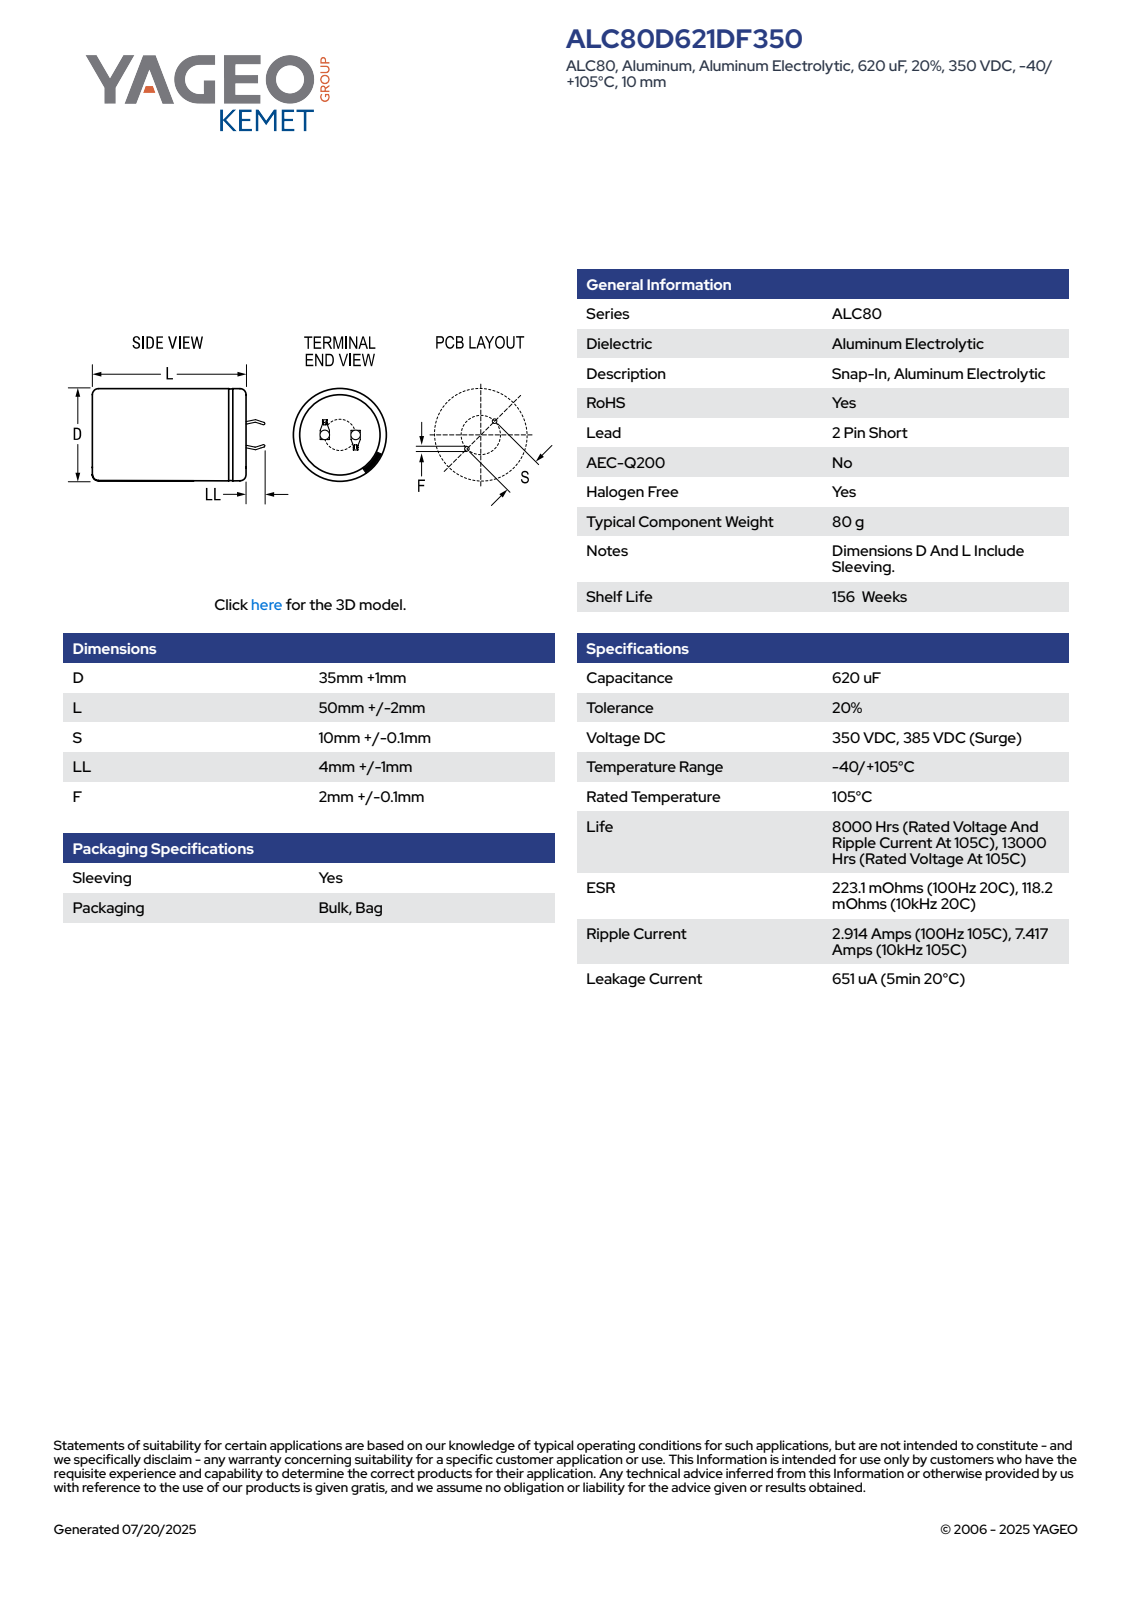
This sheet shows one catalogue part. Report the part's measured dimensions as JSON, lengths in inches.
{"part_name": "CARS_K2P_35X50_D36L52S10LL5F2.1", "step_written_by": "SolidWorks 2014 (AUTOMOTIVE_DESIGN)", "units": "inches", "bodies": {"solids": 1, "faces": 100, "planar": 52, "cylindrical": 9, "other": 39}, "overall_size": [2.244, 1.417, 1.417], "volume_in3": 3.198, "surface_area_in2": 12.25, "round_holes": [[1.254, 1]], "round_bosses_or_shafts": [[1.417, 1]], "partial_cylinders_radius": [[0.708, 1]], "face_to_face_distances": [2.047, 2.067, 0.02, 0.279, 0.024, 0.023, 0.299, 0.03, 0.053, 0.302]}
